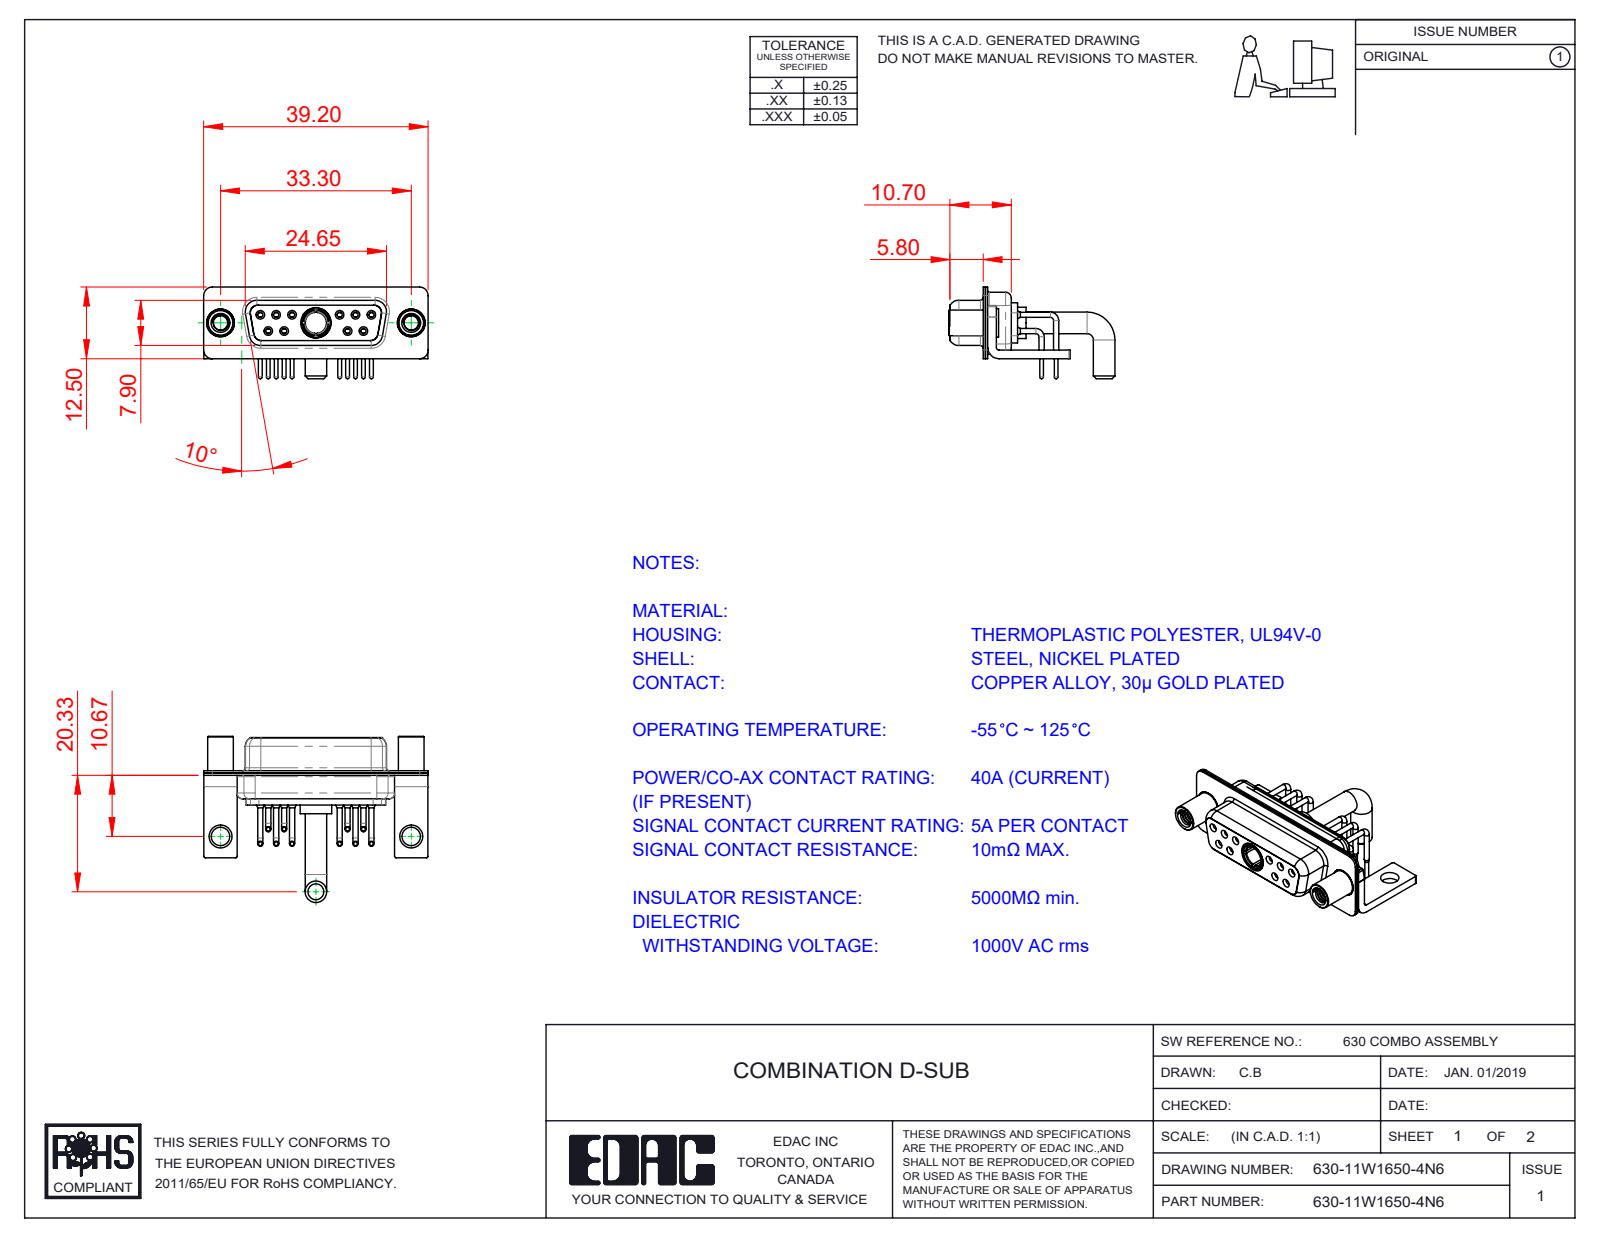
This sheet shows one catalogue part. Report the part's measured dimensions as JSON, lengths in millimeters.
{"part_name": "630Combo Contact Row 2; 630Combo Threaded Standoff_D; 630Combo Housing_11W1; 630-11W1650-4N6 (+5 more)", "step_written_by": "SolidWorks 2020 (CONFIG_CONTROL_DESIGN)", "units": "millimeters", "bodies": {"solids": 19, "faces": 985, "planar": 268, "cylindrical": 464, "other": 253}, "overall_size": [39.2, 29, 16], "volume_mm3": 3181, "surface_area_mm2": 7324, "round_holes": [[0.9, 10], [1.1, 10], [1.5, 10], [2, 10], [1.7, 6], [1.6, 4], [4.85, 3], [2.5, 2], [3.2, 2], [4, 2], [4.05, 2], [3.7, 1]], "round_bosses_or_shafts": [[0.9, 10], [0.65, 10], [1.6, 6], [5, 2], [4.95, 2], [4.8, 2], [4.5, 2], [3.75, 2]], "partial_cylinders_radius": [[0.25, 16], [1.5, 16], [2, 13], [1.35, 12], [1.6, 8], [0.5, 5], [0.6, 4], [0.65, 4]], "face_to_face_distances": [0.4, 0.8, 1.4, 0.45, 8.45, 1.5, 1.8, 8.9, 6.2, 2.3], "hole_center_spacings": [3.16, 2.77, 13.85, 11.08, 16.62, 5.03, 5.04, 5.54]}
